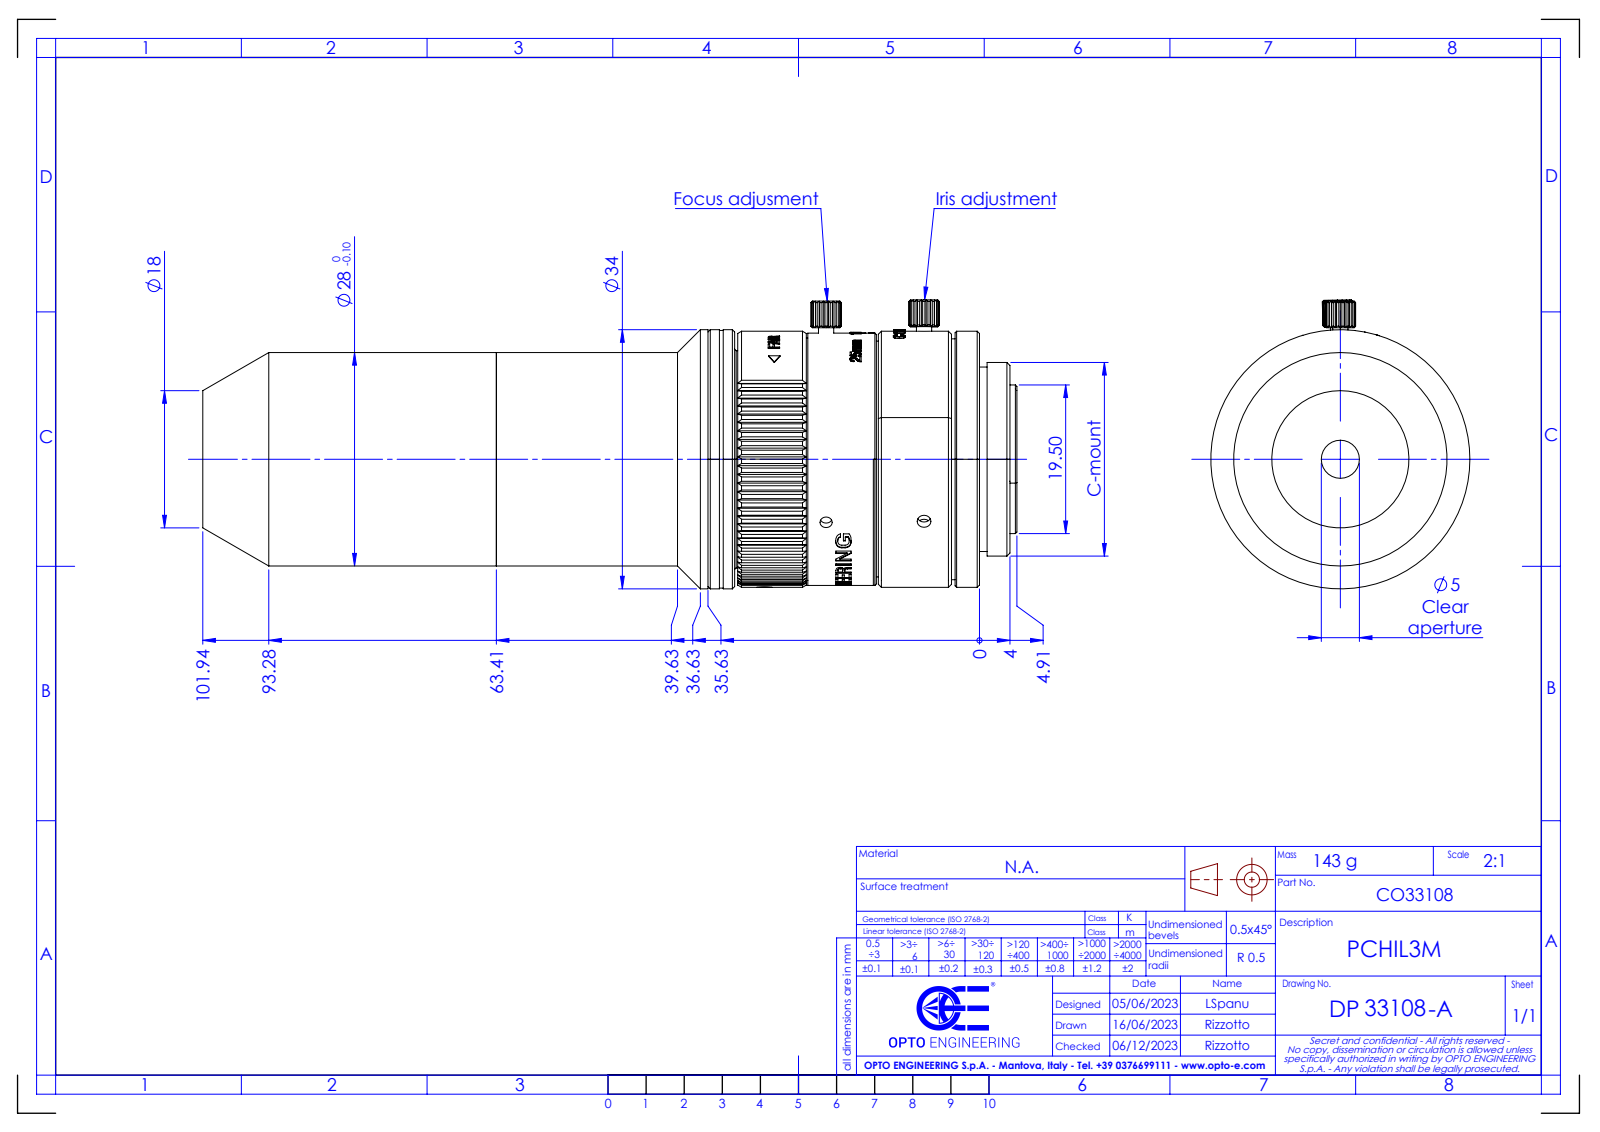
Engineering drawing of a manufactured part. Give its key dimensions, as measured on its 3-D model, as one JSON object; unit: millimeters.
{"part_name": "DP33108-A_PCHIL3M", "step_written_by": "SolidWorks 2021 (CONFIG_CONTROL_DESIGN)", "units": "millimeters", "bodies": {"solids": 0, "faces": 853, "planar": 374, "cylindrical": 209, "other": 270}, "overall_size": [106.85, 37.92, 34], "round_holes": [[2, 3], [1.6, 2], [1.8, 2], [5, 1], [14, 1], [22.8, 1]], "round_bosses_or_shafts": [[34, 1], [33.8, 1], [33.6, 1], [33.1, 1], [31.6, 1], [28, 1], [27, 1], [25.4, 1]], "partial_cylinders_radius": [[1, 2], [2, 2], [16.45, 1], [16.61, 1], [16.64, 1], [16.65, 1]], "face_to_face_distances": [0.55, 101.39, 101.94, 69.81, 31.58, 32.13, 66.31, 3.5, 35.08, 35.63], "hole_center_spacings": [14, 24.24]}
